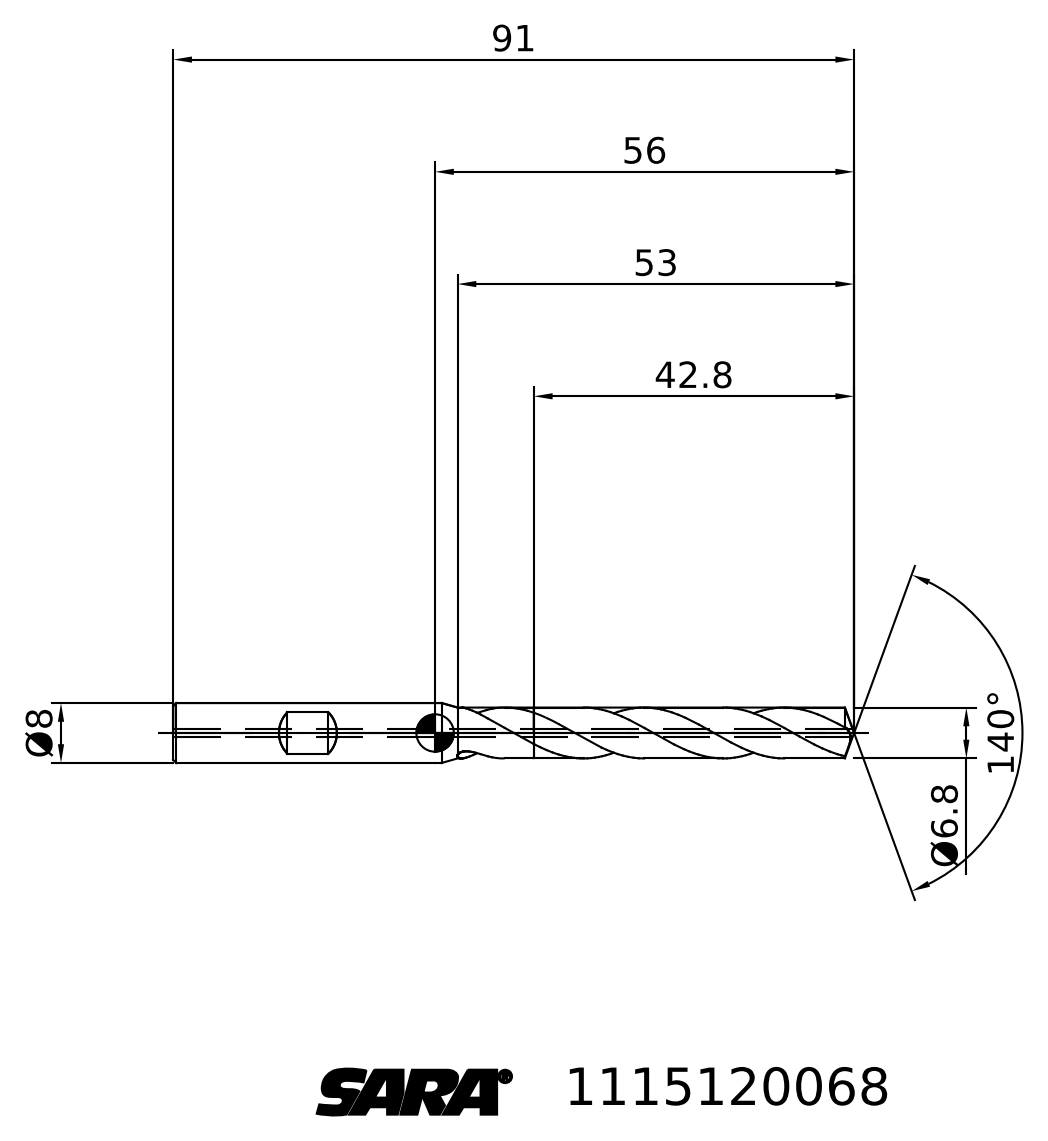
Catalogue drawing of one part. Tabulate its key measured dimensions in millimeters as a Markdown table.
| quantity | value |
| --- | --- |
| STEP written by | TDM (AUTOMOTIVE_DESIGN) |
| units | millimeters |
| bodies | 2 solids, 31 faces (6 planar, 0 cylindrical, 25 other) |
| overall size | 91 × 15.79 × 10.6 |
| volume | 3 133 mm³ |
| surface area | 2 284 mm² |
| main face-to-face distances | 48.2 |
